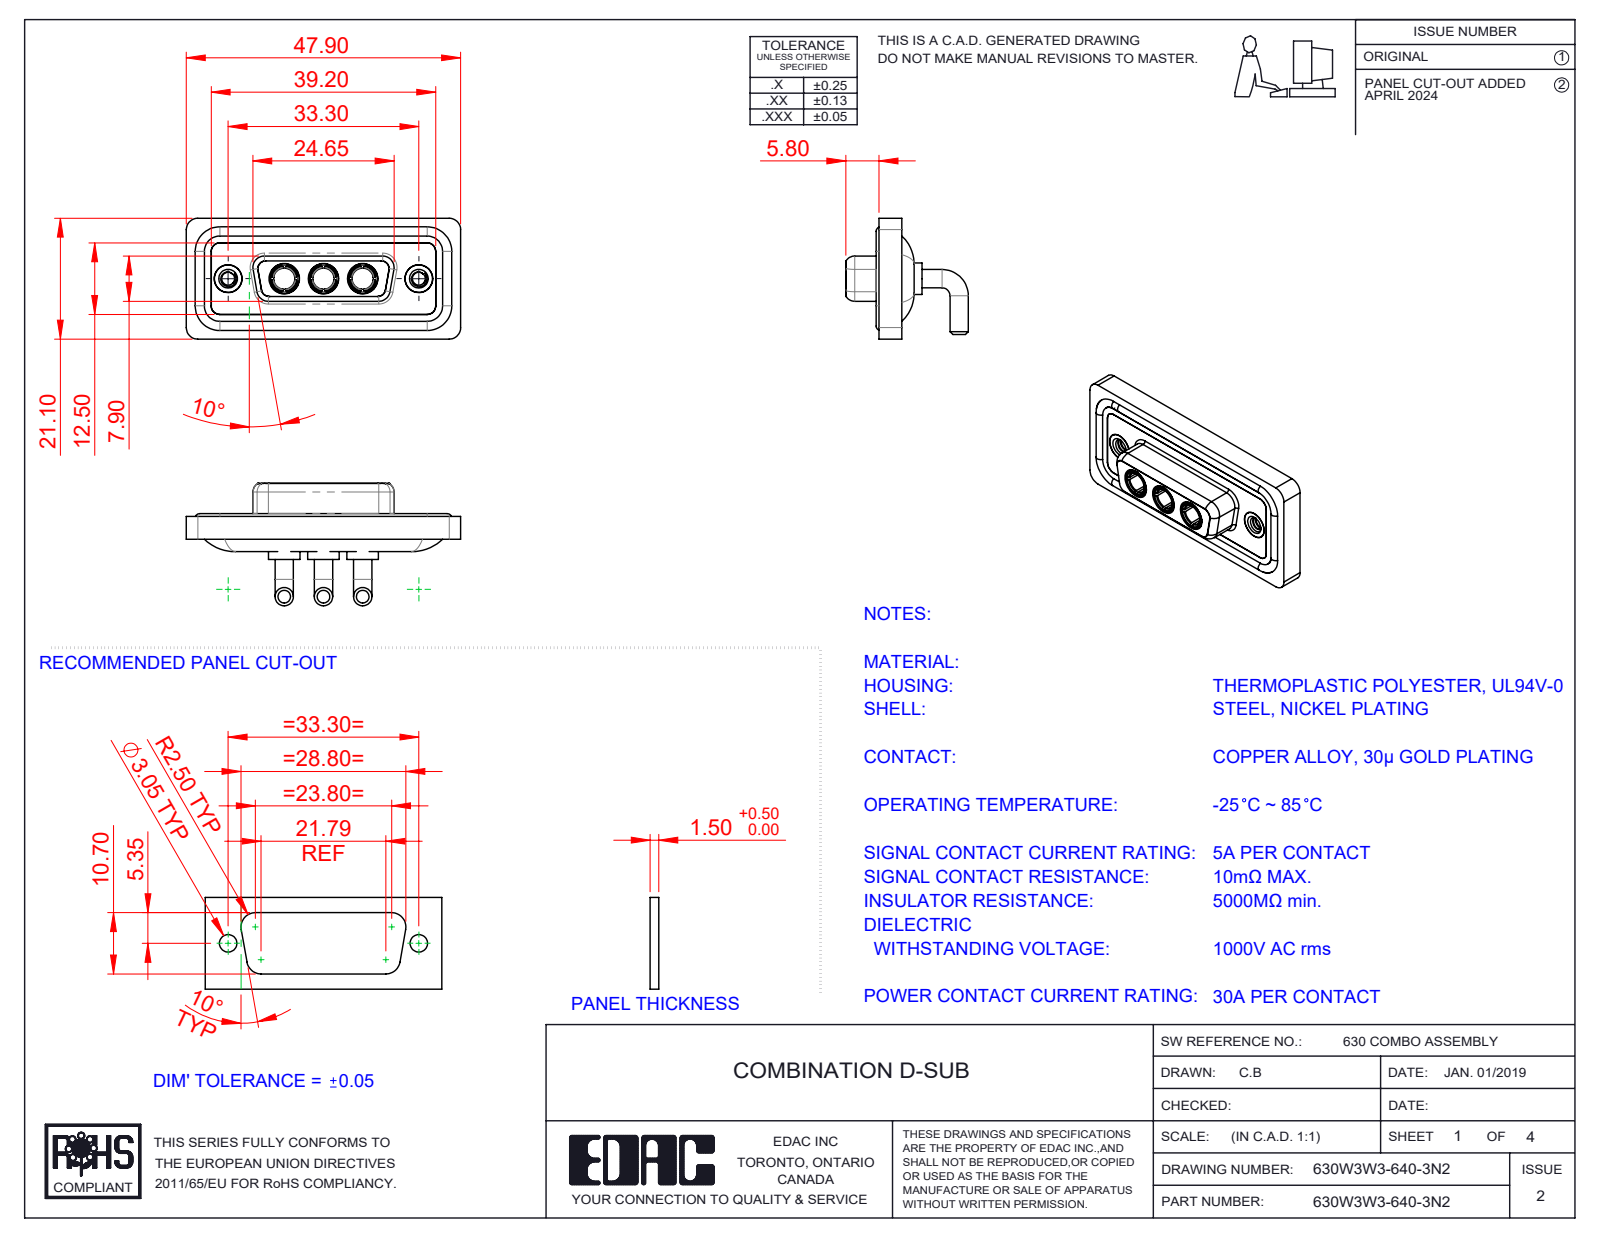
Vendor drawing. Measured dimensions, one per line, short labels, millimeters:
name: 630Combo Housing_3W3; 630W3W3-640-3N2; 630Combo Threaded Rivet_2; 630Combo Waterproof Housing_15 Contacts (+3 more)
written by: SolidWorks 2023 (CONFIG_CONTROL_DESIGN)
unit: mm
bodies: 13 solids, 620 faces (192 planar, 263 cylindrical, 165 other)
size: 47.9 × 21.4 × 21.1
volume: 6 264 mm³; area: 10 027 mm²
holes: 5× ⌀4.85, 3× ⌀3.7, 3× ⌀5.3, 2× ⌀2.26, 2× ⌀4, 2× ⌀4.05, 2× ⌀5
bosses: 6× ⌀3.2, 4× ⌀1.6, 3× ⌀5.5, 3× ⌀5.2, 3× ⌀4.96, 3× ⌀4.75, 3× ⌀3.75, 2× ⌀4.95
rounds: 20× R2, 18× R1.5, 12× R1.35, 8× R1.6, 4× R0.25, 4× R0.5, 4× R0.6, 4× R0.65
face distances: 0.4, 1.8, 1.1, 1.6, 2.9, 2.5, 3.1, 3.7, 4.1, 1.5
hole spacings: 6.85, 9.8, 16.65, 23.5, 13.7, 33.3
